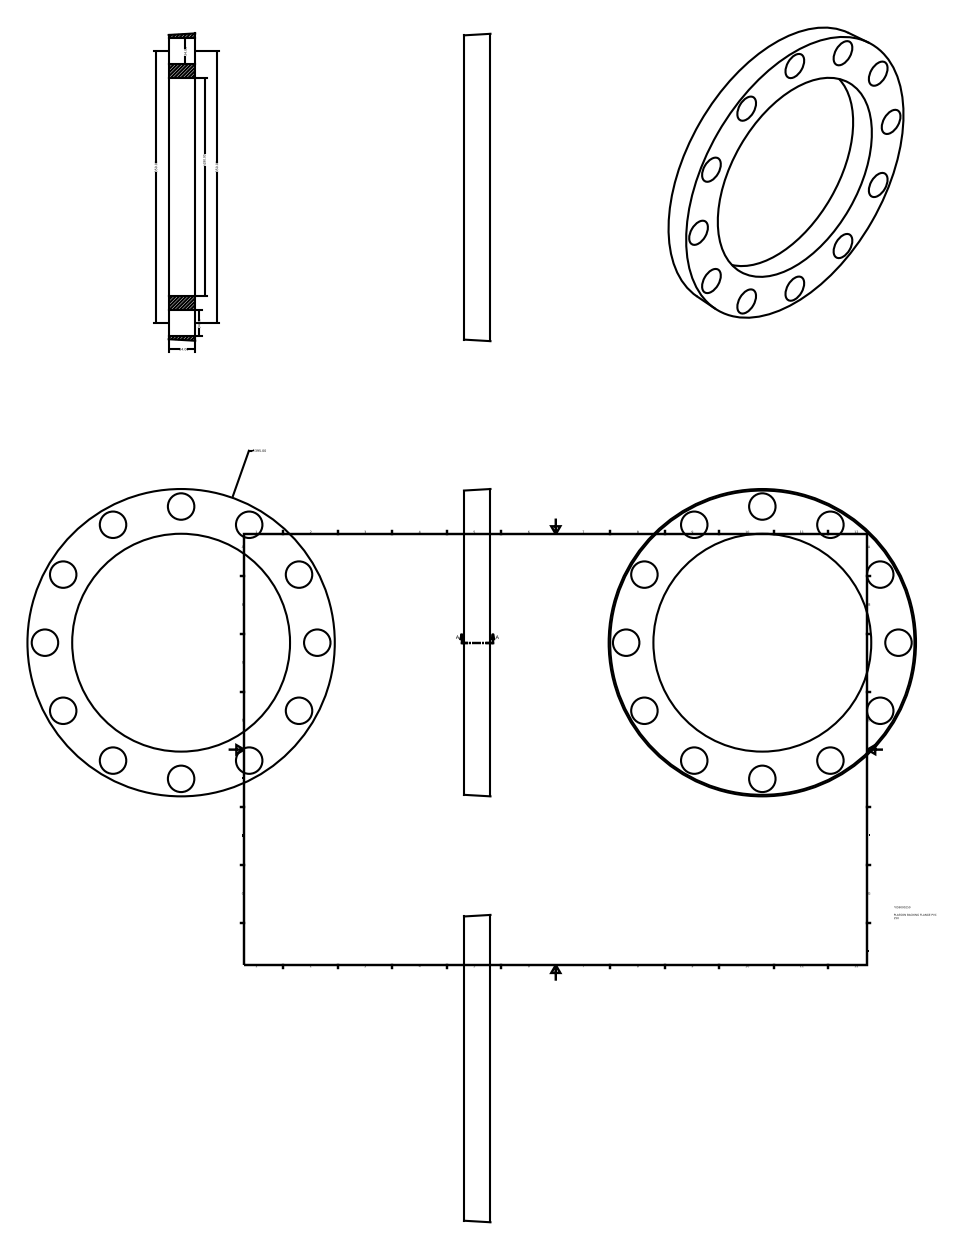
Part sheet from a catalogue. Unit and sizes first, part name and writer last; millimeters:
Units: millimetres
Overall size (bounding box): 395 × 395 × 34
Round holes (diameter × count): ⌀34 ×12, ⌀280 ×1
Main face-to-face distances: 34
Hole centre spacings: 175, 338.07, 90.59, 247.48, 303.11, 90.58, 247.49, 303.1
Volume: 1 661 000 mm³ · Surface area: 213 244 mm²
Bodies: 1 solid, 16 faces (2 planar, 13 cylindrical, 1 other)
Part name (STEP PRODUCT): (_AS)059000250
STEP written by: Autodesk Inventor 2015 (AUTOMOTIVE_DESIGN)
